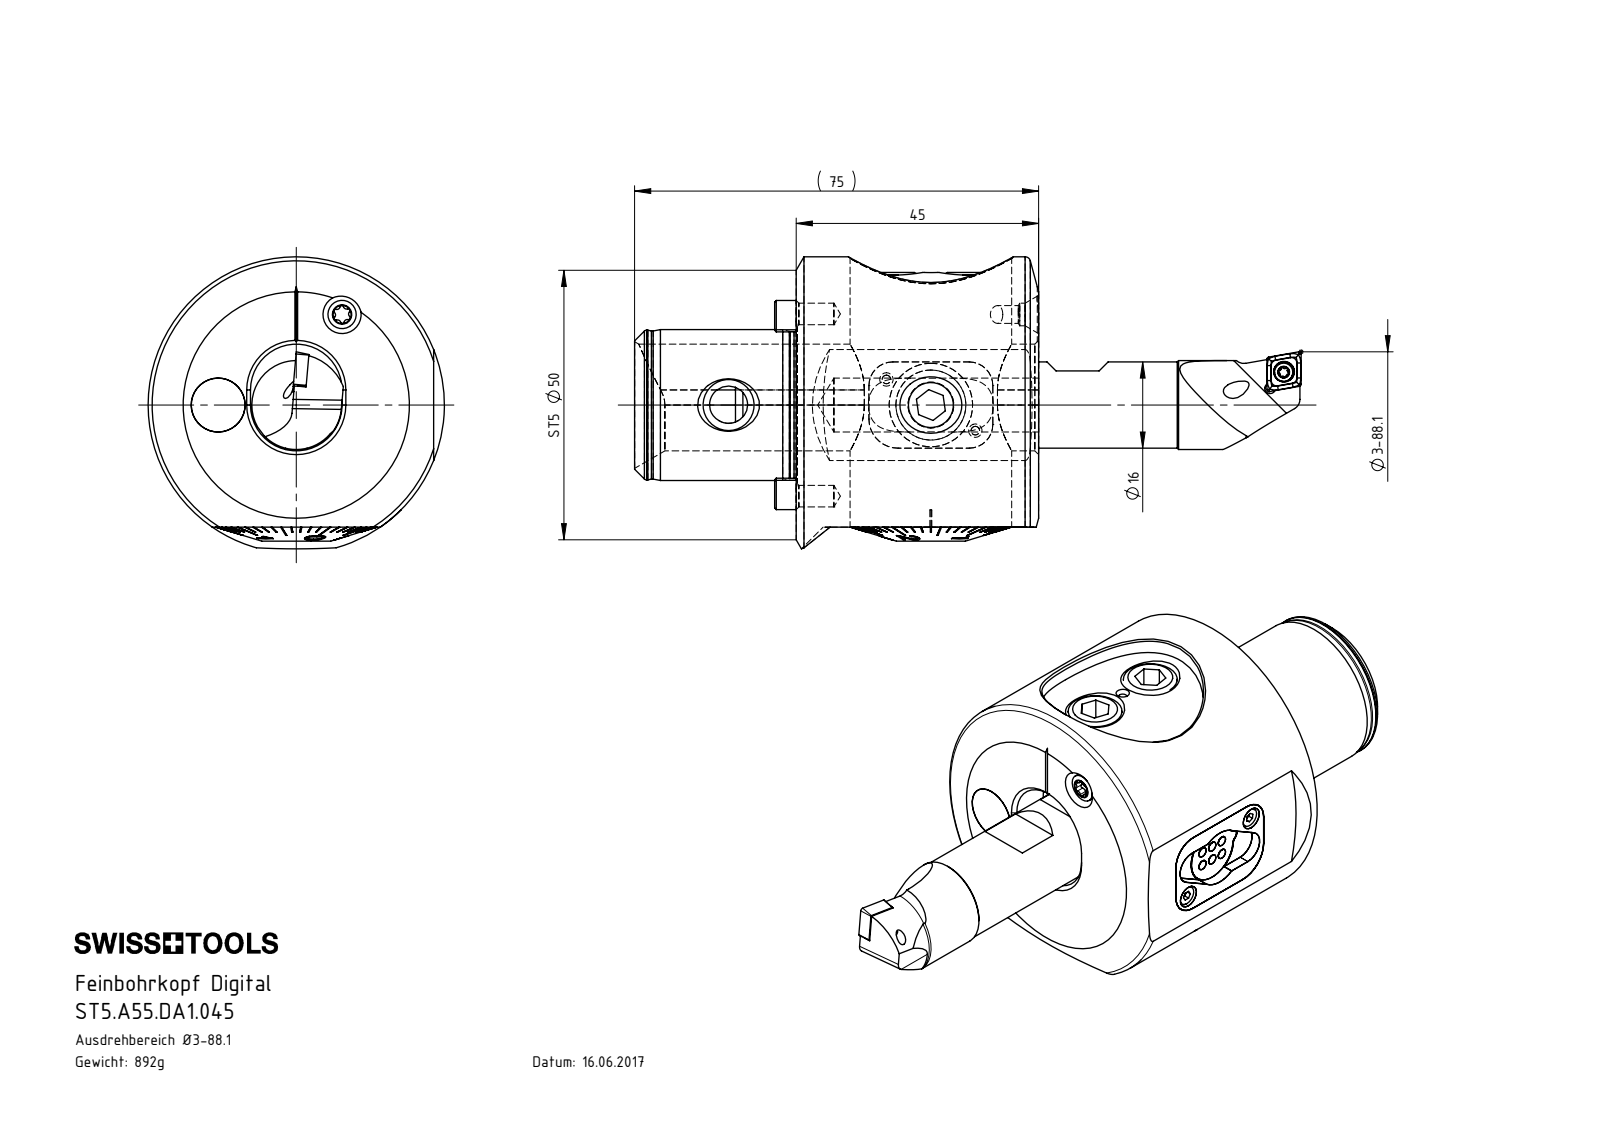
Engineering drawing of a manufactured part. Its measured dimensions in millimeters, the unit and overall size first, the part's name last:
Units: millimetres
Overall size (bounding box): 131 × 123.73 × 54.18
Round holes (diameter × count): ⌀2 ×4, ⌀1.5 ×3, ⌀1.6 ×3, ⌀1.88 ×3, ⌀2.5 ×3, ⌀4.2 ×3, ⌀8.5 ×3, ⌀2.2 ×2, ⌀3 ×2, ⌀4 ×2, ⌀5.2 ×2, ⌀0.8 ×1
Round bosses / shafts (diameter × count): ⌀1.9 ×6, ⌀1.38 ×6, ⌀1.07 ×6, ⌀0.8 ×6, ⌀10 ×3, ⌀4.8 ×3, ⌀3.2 ×3, ⌀2.25 ×3
Partial cylindrical surfaces — rounded edges, fillets, slot ends (radius × count): R0.4 ×49, R0.5 ×45, R0.1 ×38, R0.2 ×34, R0.3 ×30, R0.14 ×27, R0.6 ×26, R1.1 ×18
Main face-to-face distances: 1.55, 45, 2, 4, 3.7, 1.1, 5.3, 2.8, 1, 6.85
Hole centre spacings: 58.16, 57.72, 4.32, 15.24, 63.34, 5.2, 7.25, 9.13
Volume: 135 272 mm³ · Surface area: 71 463 mm²
Bodies: 54 solids, 4450 faces (1043 planar, 898 cylindrical, 2509 other)
Part name (STEP PRODUCT): ISO 4762 - M2 x 6; DIN 3771 - 25x1.5; CCMT060204; TESA_Band (+8 more)
STEP written by: SolidWorks 2017 (CONFIG_CONTROL_DESIGN)
